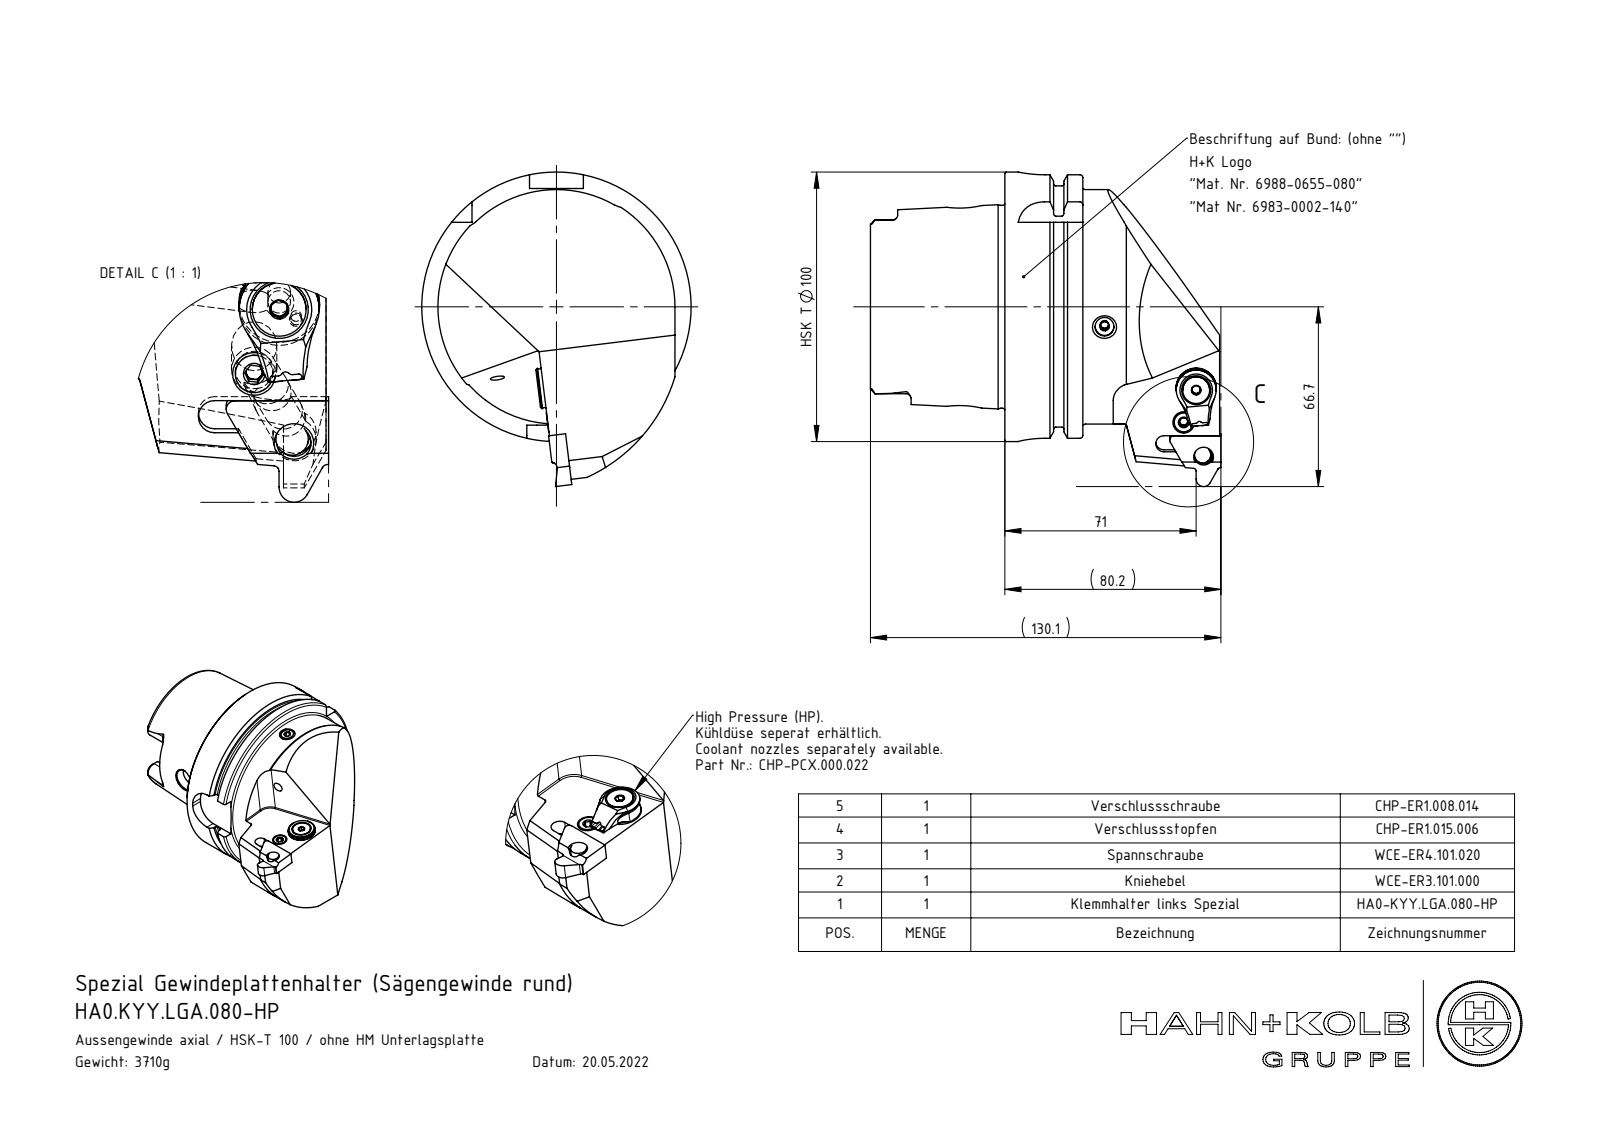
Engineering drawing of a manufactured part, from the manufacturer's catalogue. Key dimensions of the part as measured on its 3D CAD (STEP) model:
Part name (STEP PRODUCT): WCE-ER3.101.000_A; CHP-PCX.000.022_B; DIN 3771 - 13x1; CHP-PCX.000.022_Dse (+8 more)
STEP written by: SolidWorks 2017 (AUTOMOTIVE_DESIGN)
Units: millimetres
Bodies: 12 solids, 428 faces (152 planar, 116 cylindrical, 160 other)
Overall size (bounding box): 130.1 × 116.69 × 100
Volume: 473 248 mm³ · Surface area: 71 258 mm²
Round holes (diameter × count): ⌀5 ×4, ⌀4.2 ×2, ⌀7 ×2, ⌀12 ×2, ⌀1.2 ×1, ⌀2 ×1, ⌀3 ×1, ⌀5.3 ×1, ⌀6 ×1, ⌀6.35 ×1, ⌀8.4 ×1, ⌀10 ×1
Round bosses / shafts (diameter × count): ⌀8 ×2, ⌀6 ×2, ⌀100 ×1, ⌀91.95 ×1, ⌀87 ×1, ⌀75.26 ×1, ⌀14.85 ×1, ⌀13.4 ×1
Partial cylindrical surfaces — rounded edges, fillets, slot ends (radius × count): R1 ×9, R1.9 ×6, R0.5 ×4, R4.88 ×4, R10 ×4, R0.3 ×3, R3.5 ×3, R6 ×3
Main face-to-face distances: 79.73, 12.45, 67.28, 28.95, 16.5, 50.78, 49.9, 62.35, 78.85, 129.63
Hole centre spacings: 4.49, 4.5, 12.35, 13.65, 22.53, 25.91, 14.89
